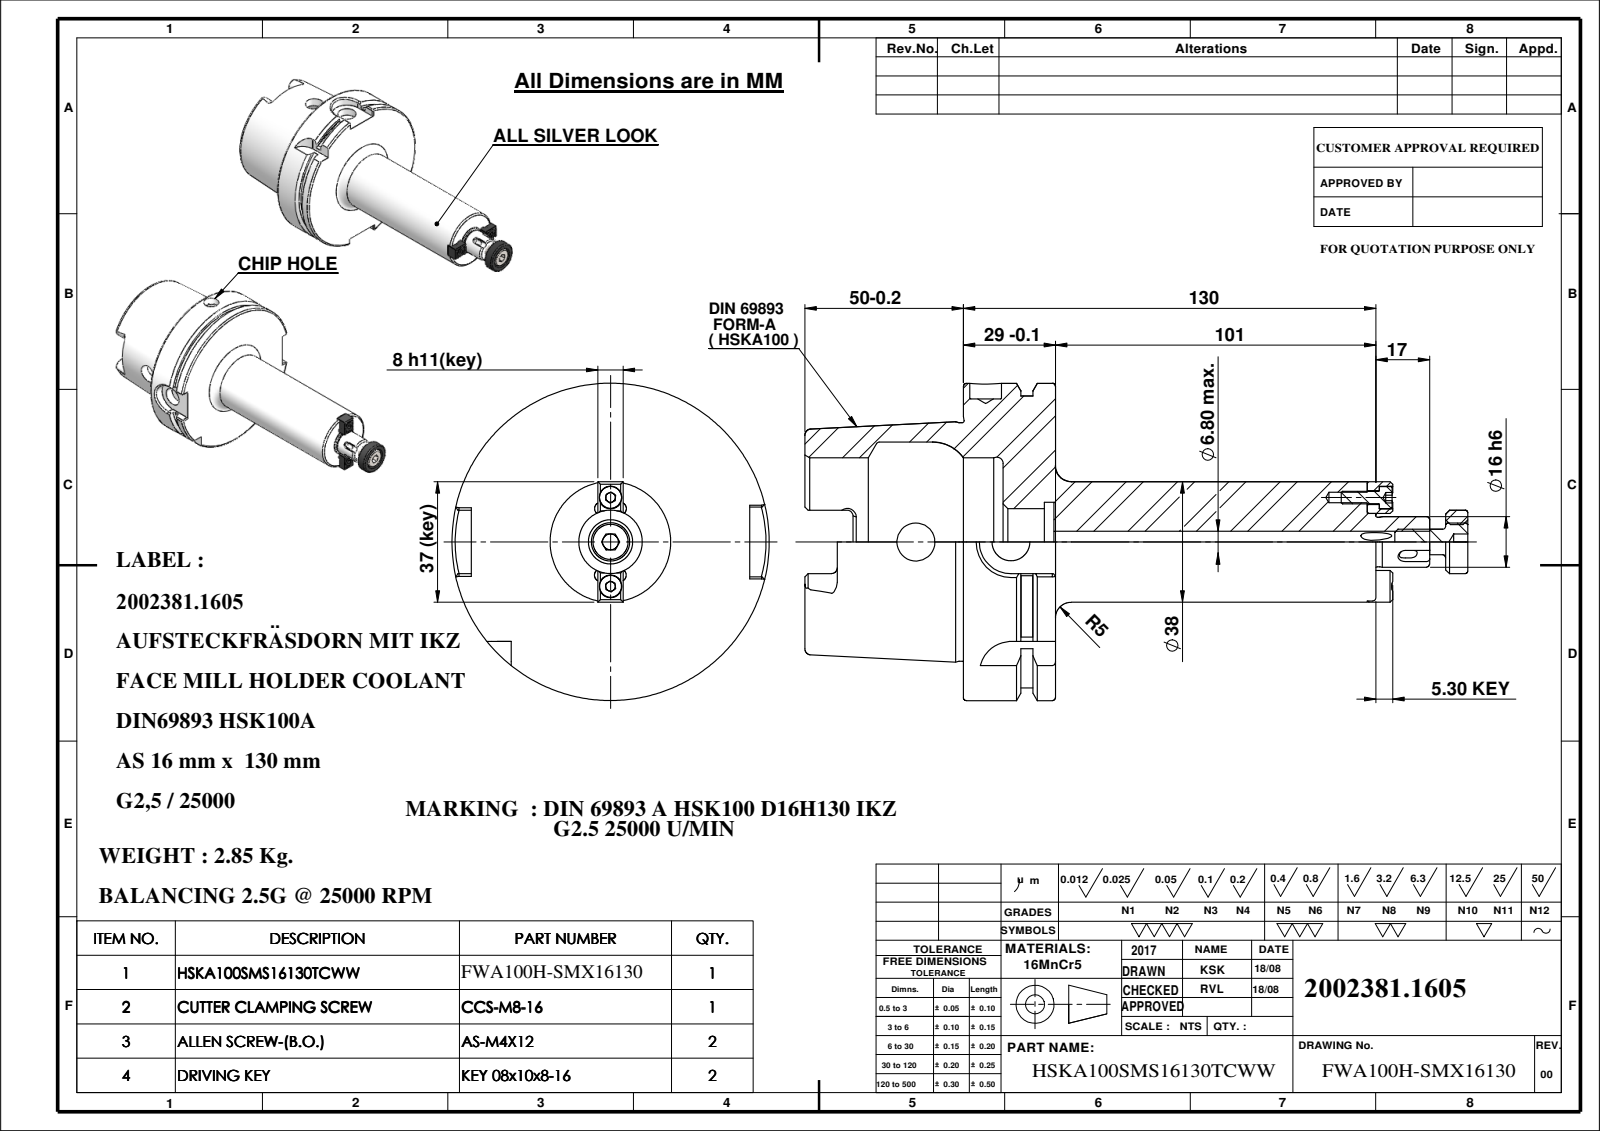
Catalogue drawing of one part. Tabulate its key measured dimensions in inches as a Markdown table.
| quantity | value |
| --- | --- |
| part name | CCS-M8-16-SHORT LENGHT; 91100A-AS516130; HSKA100SMS16130TCWW; CCS-M8-16-1-SHORT LENGHT (+3 more) |
| STEP written by | SolidWorks 2009 (CONFIG_CONTROL_DESIGN) |
| units | inches |
| bodies | 7 solids, 383 faces (153 planar, 100 cylindrical, 130 other) |
| overall size | 8.228 × 3.937 × 3.937 |
| volume | 22.66 in³ |
| surface area | 107.4 in² |
| round holes (diameter × count) | 0.118 × 4, 0.13 × 2, 0.173 × 2, 0.28 × 2, 0.472 × 2, 0.268 × 1, 0.394 × 1, 0.433 × 1, 0.827 × 1, 0.984 × 1, 2.087 × 1, 2.48 × 1 |
| round bosses / shafts (diameter × count) | 0.276 × 2, 0.157 × 2, 3.937 × 1, 3.622 × 1, 2.959 × 1, 1.496 × 1, 0.787 × 1, 0.63 × 1 |
| partial cylindrical surfaces (radius × count) | 0.079 × 8, 0.071 × 6, 0.192 × 4, 0.394 × 2, 0.433 × 1 |
| main face-to-face distances | 1.142, 0.492, 0.65, 1.969, 2.461, 3.11, 5.118, 7.087, 4.626, 3.976 |
| hole center spacings | 0.551, 1.102, 1.181 |
